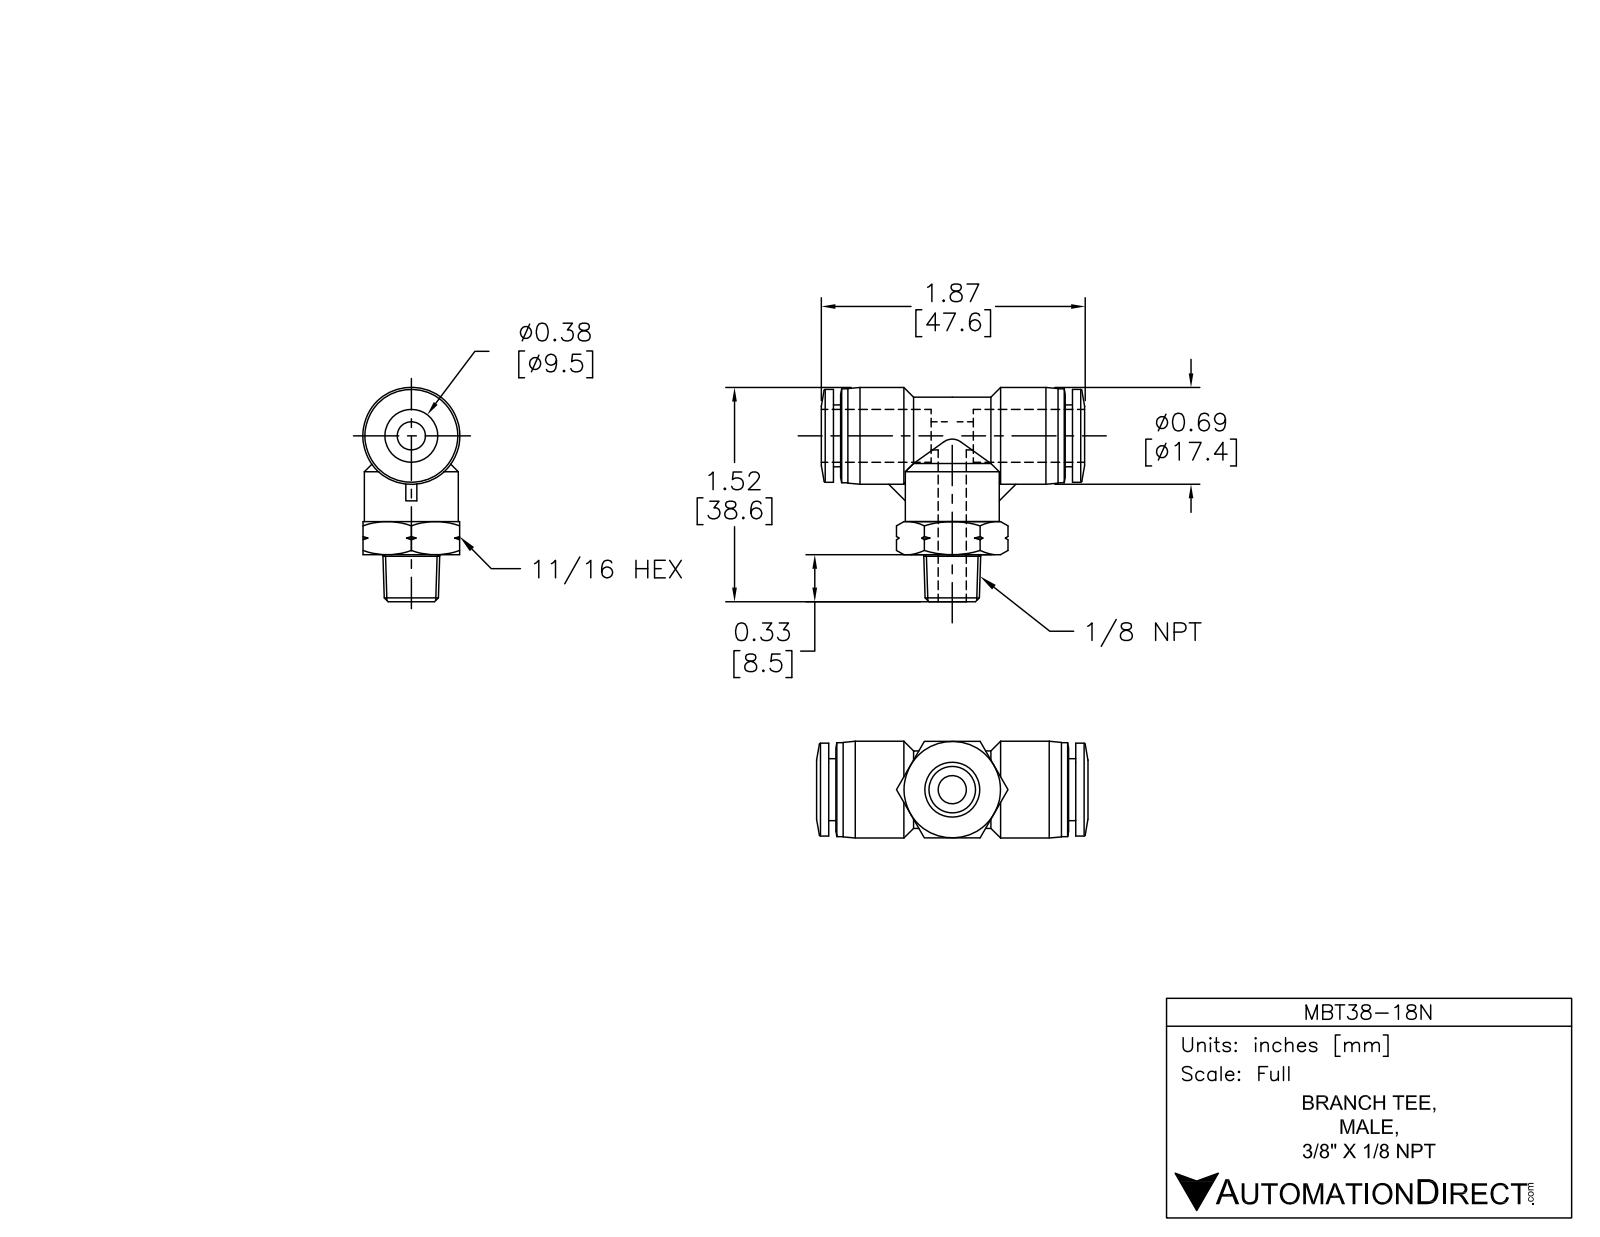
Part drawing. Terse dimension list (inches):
name: MBT38-18N
written by: SolidWorks 2015 (AUTOMOTIVE_DESIGN)
unit: in
bodies: 1 solid, 115 faces (23 planar, 31 cylindrical, 61 other)
size: 1.874 × 1.526 × 0.689
volume: 0.626 in³; area: 9.704 in²
holes: 2× ⌀0.197, 1× ⌀0.386
bosses: 2× ⌀0.669, 1× ⌀0.689, 1× ⌀0.661, 1× ⌀0.441
rounds: 2× R0.276
face distances: 0.687, 0.051, 1.65, 1.701, 0.705, 0.996, 0.654, 0.945, 1.598, 0.291
